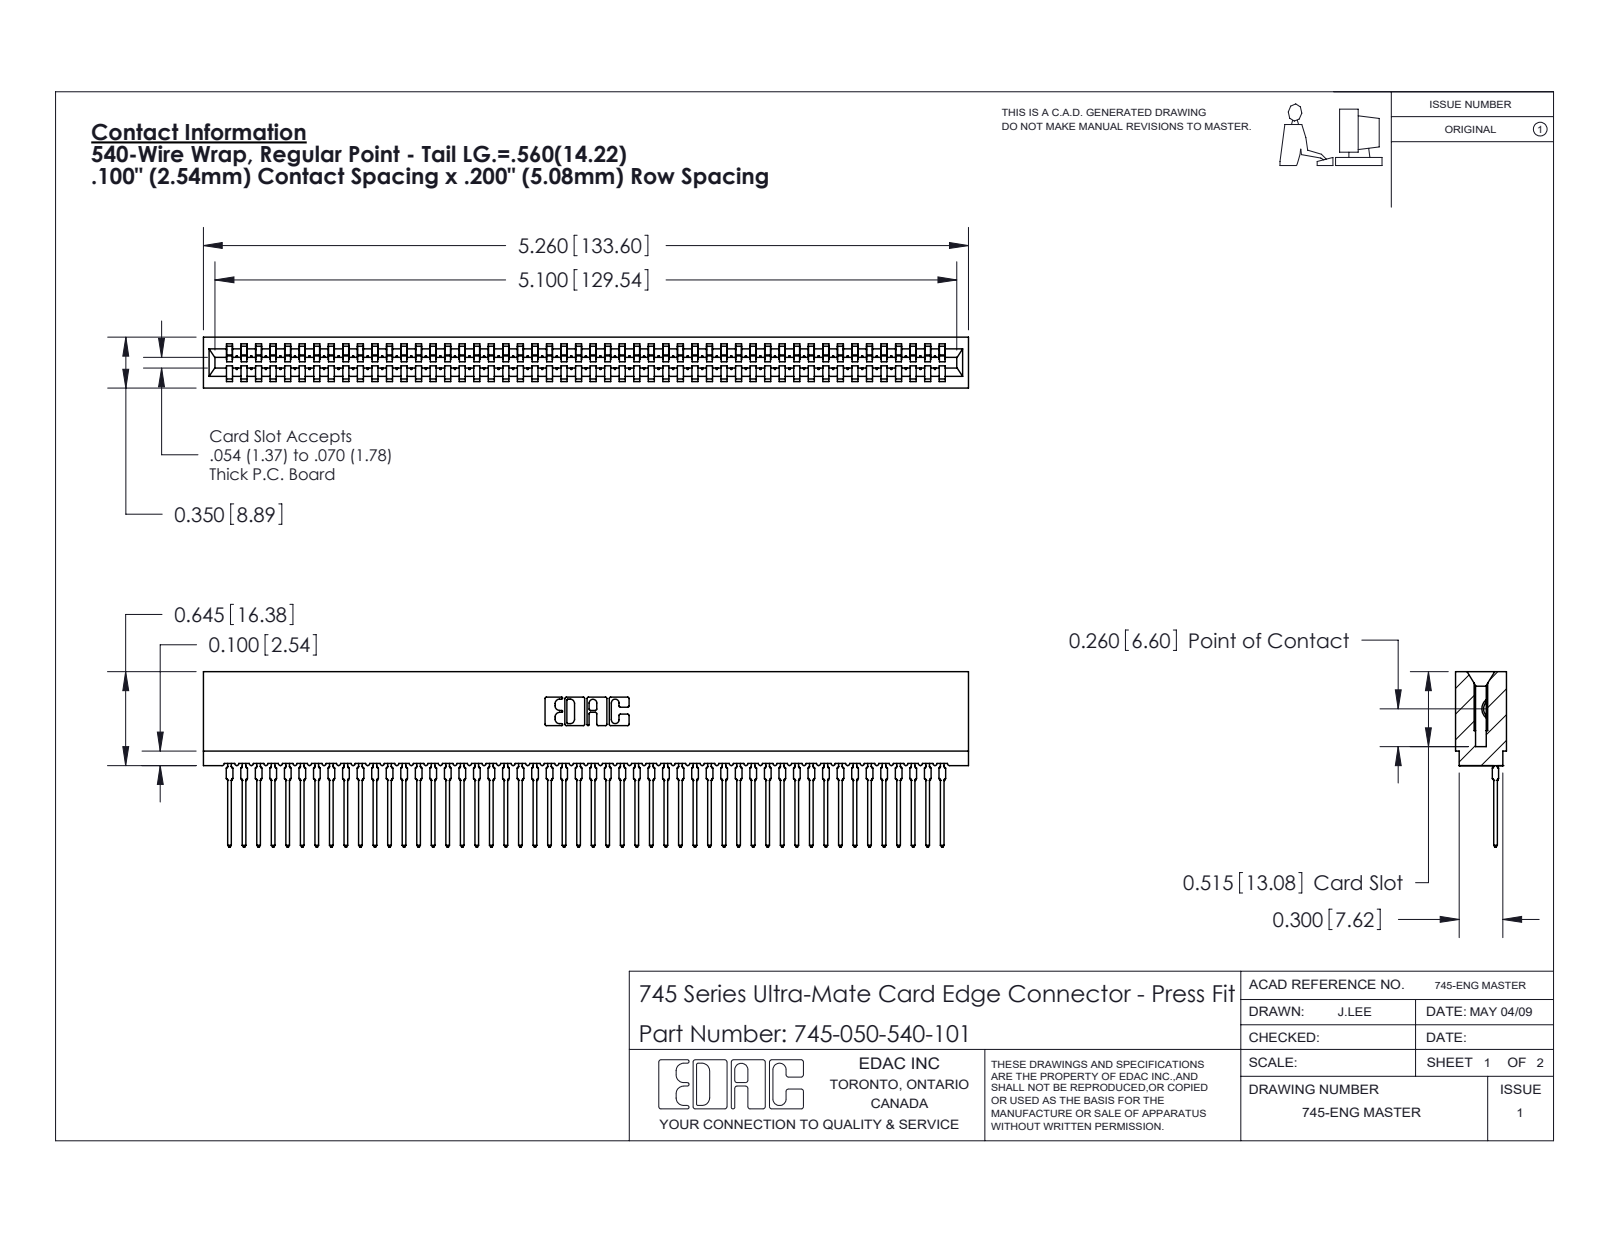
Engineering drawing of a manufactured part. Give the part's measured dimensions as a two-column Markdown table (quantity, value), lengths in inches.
| quantity | value |
| --- | --- |
| part name | 745 Part_Insulator Option - 01; 745-292-001_540; 745-050-540-101 |
| STEP written by | SolidWorks 2020 (CONFIG_CONTROL_DESIGN) |
| units | inches |
| bodies | 51 solids, 5695 faces (3405 planar, 990 cylindrical, 1300 other) |
| overall size | 5.26 × 1.206 × 0.35 |
| volume | 0.71 in³ |
| surface area | 34.72 in² |
| partial cylindrical surfaces (radius × count) | 0.015 × 100, 0.021 × 100, 0.01 × 22, 0.007 × 6, 0.031 × 6, 0.005 × 4, 0.011 × 4, 0.026 × 3 |
| main face-to-face distances | 0.35, 0.045, 0.305, 0.138, 0.212, 0.093, 0.167, 0.063, 0.287, 0.243 |
